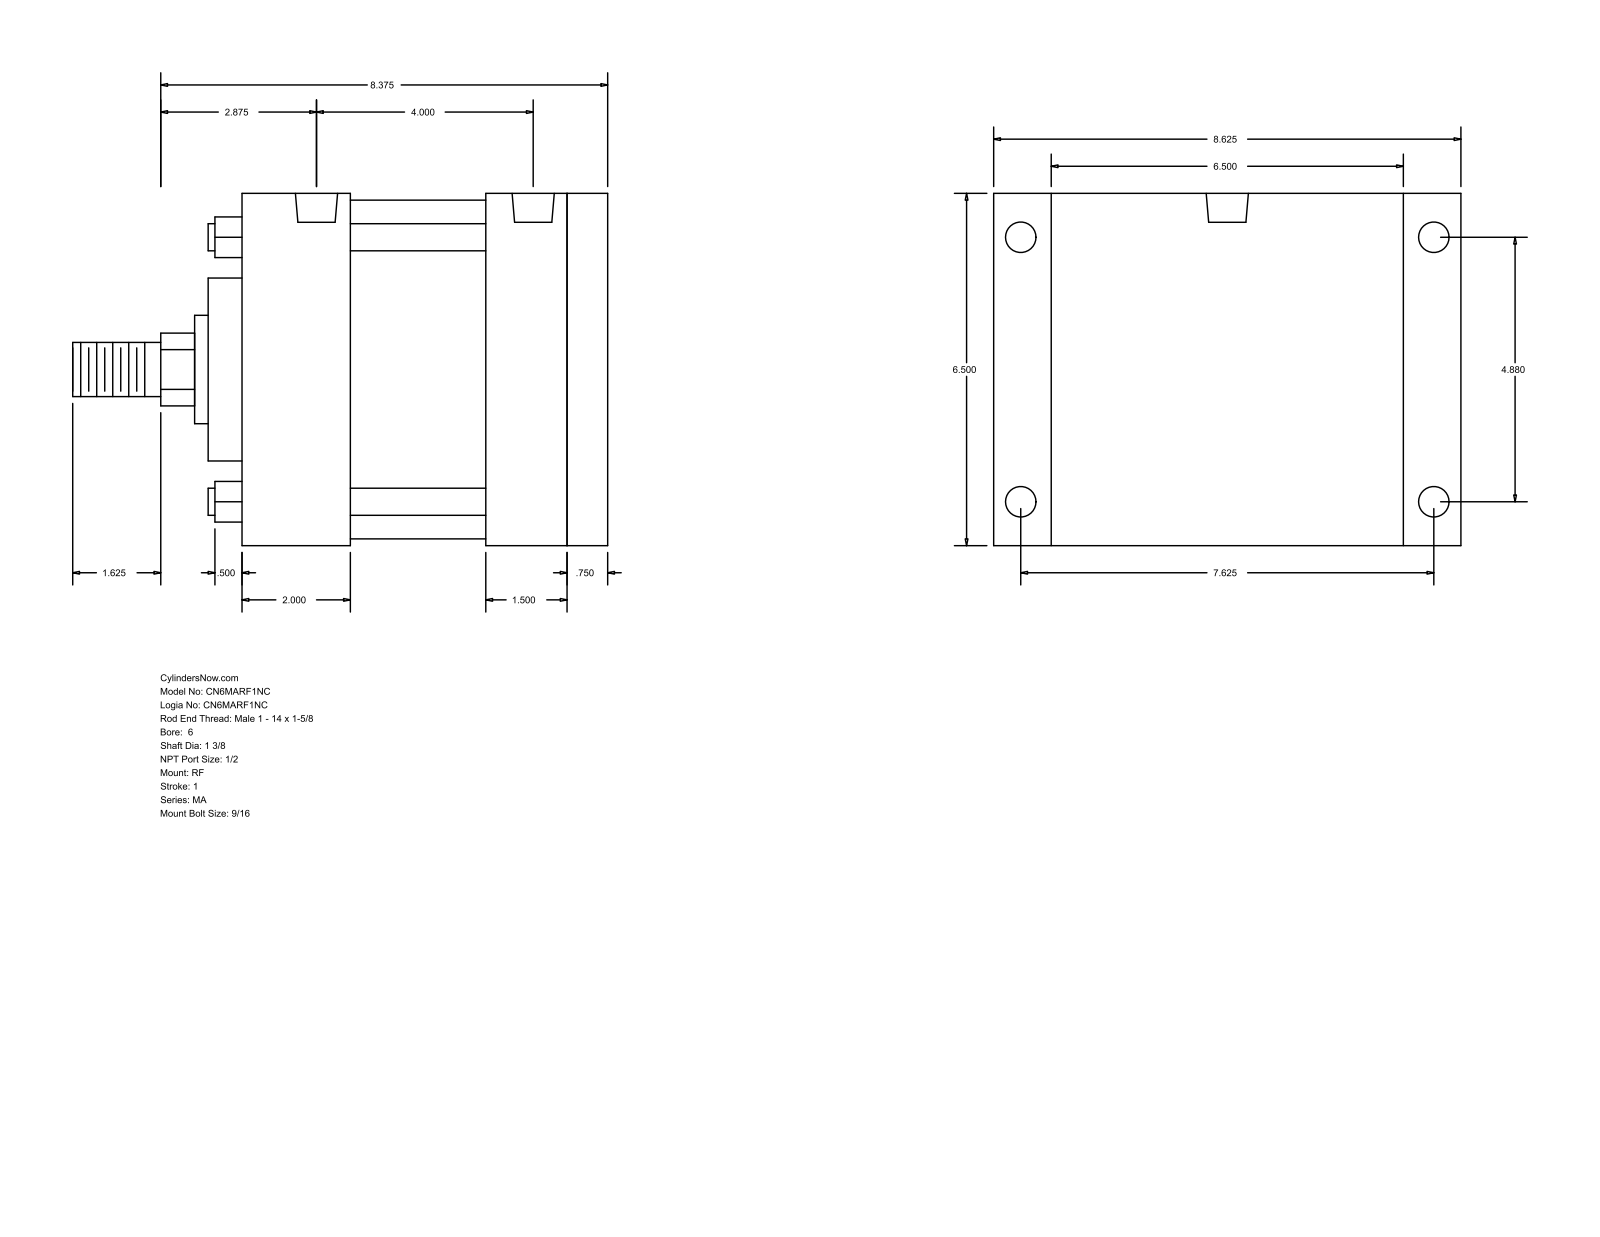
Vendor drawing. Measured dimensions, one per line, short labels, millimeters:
name: MA_RF__0600_1.375
written by: GSSL Pune (CONFIG_CONTROL_DESIGN)
unit: mm
bodies: 0 solids, 94 faces (65 planar, 29 cylindrical, 0 other)
size: 254 × 219.07 × 165.1
holes: 4× ⌀14.29, 4× ⌀17.46, 2× ⌀19.77
bosses: 4× ⌀12.7, 1× ⌀158.75, 1× ⌀85.72, 1× ⌀50.8, 1× ⌀34.92, 1× ⌀25.4
rounds: 1× R17.06
face distances: 165.1, 174.62, 66.67, 155.58, 19.04, 57.15, 50.8, 104.78, 123.82, 117.47
hole spacings: 104.77, 123.96, 193.68, 229.95, 3.18, 101.59
